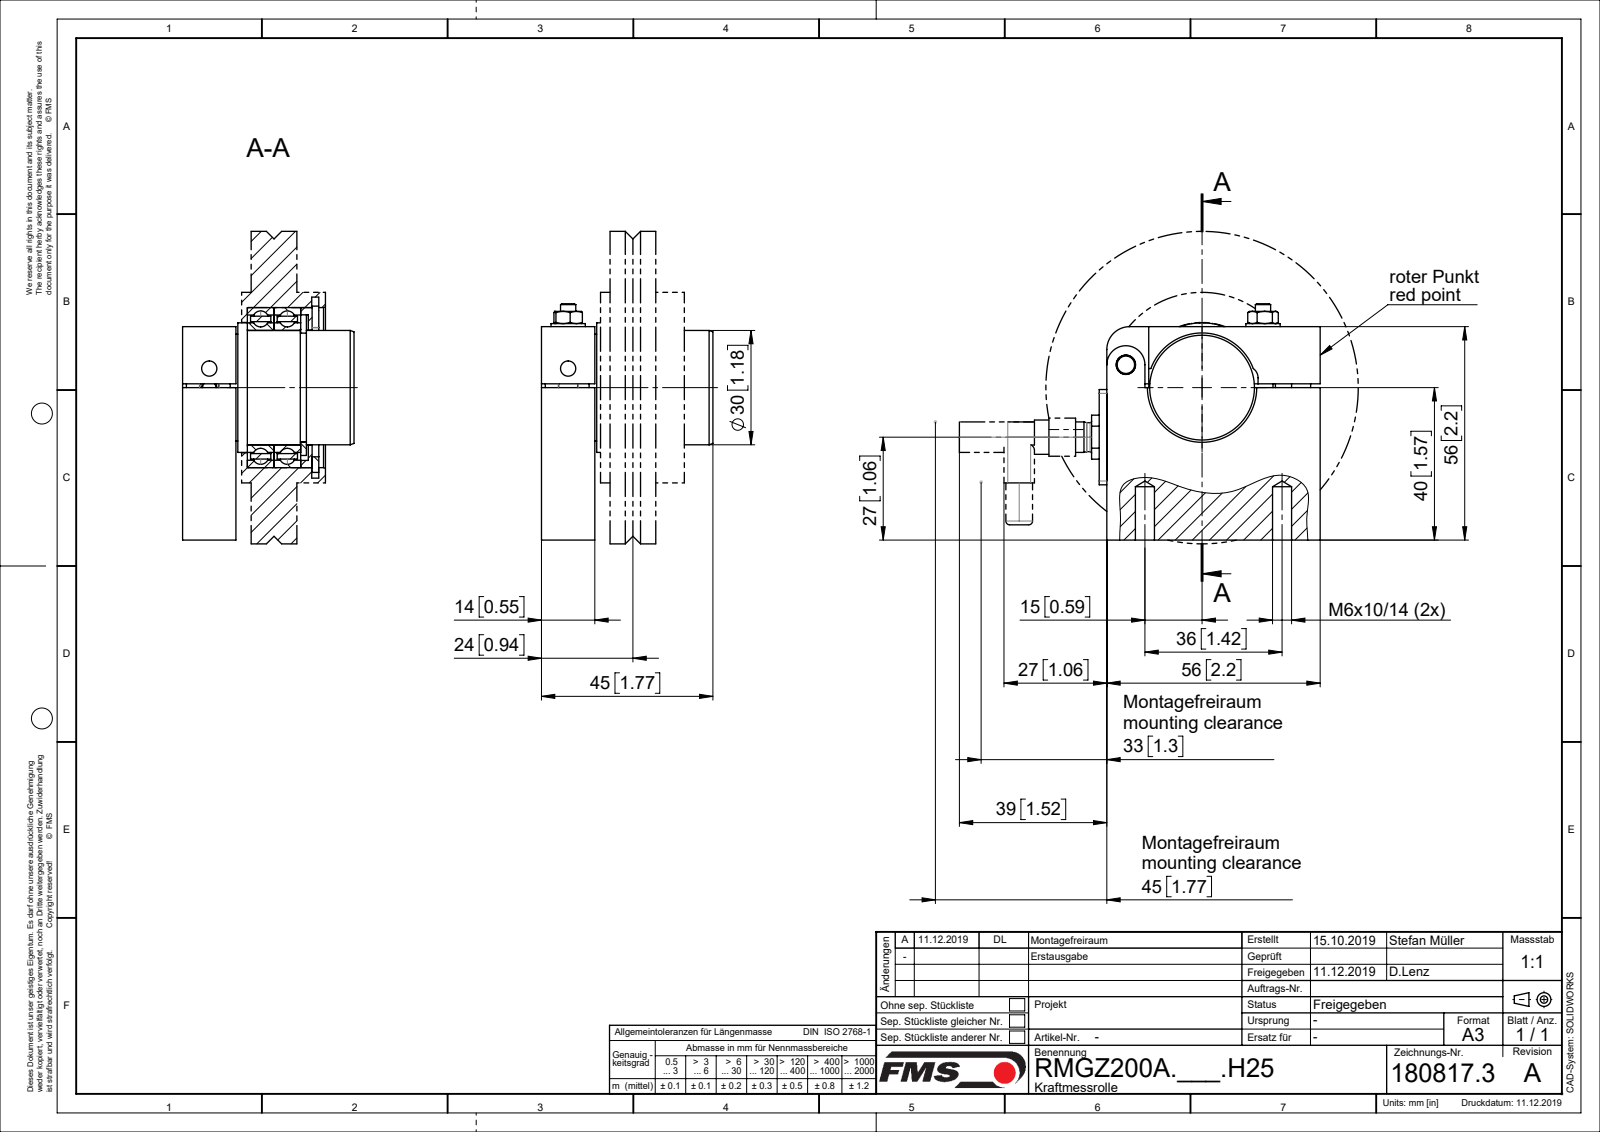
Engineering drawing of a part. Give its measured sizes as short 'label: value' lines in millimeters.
name: R1609051_H25; R1609053; R1609054; R1705151 (+8 more)
written by: Mechanical Desktop 2009 (CONFIG_CONTROL_DESIGN)
unit: mm
bodies: 21 solids, 470 faces (153 planar, 198 cylindrical, 119 other)
size: 66.5 × 62.25 × 45
volume: 70 725 mm³; area: 40 280 mm²
holes: 7× ⌀3.2, 6× ⌀2.6, 4× ⌀6.4, 3× ⌀4, 2× ⌀2.2, 2× ⌀5.15, 2× ⌀6, 1× ⌀3.42, 1× ⌀3.5, 1× ⌀4.3, 1× ⌀4.33, 1× ⌀5
bosses: 6× ⌀3, 4× ⌀5.5, 4× ⌀1, 2× ⌀8, 2× ⌀6, 1× ⌀44.5, 1× ⌀42, 1× ⌀36.4
rounds: 4× R1, 1× R2.5, 1× R3, 1× R4.1, 1× R5, 1× R6
face distances: 14, 10, 17, 7, 3, 20, 31, 34, 16, 9
hole spacings: 9, 18, 9.85, 10.3, 15.81, 5, 8, 4
